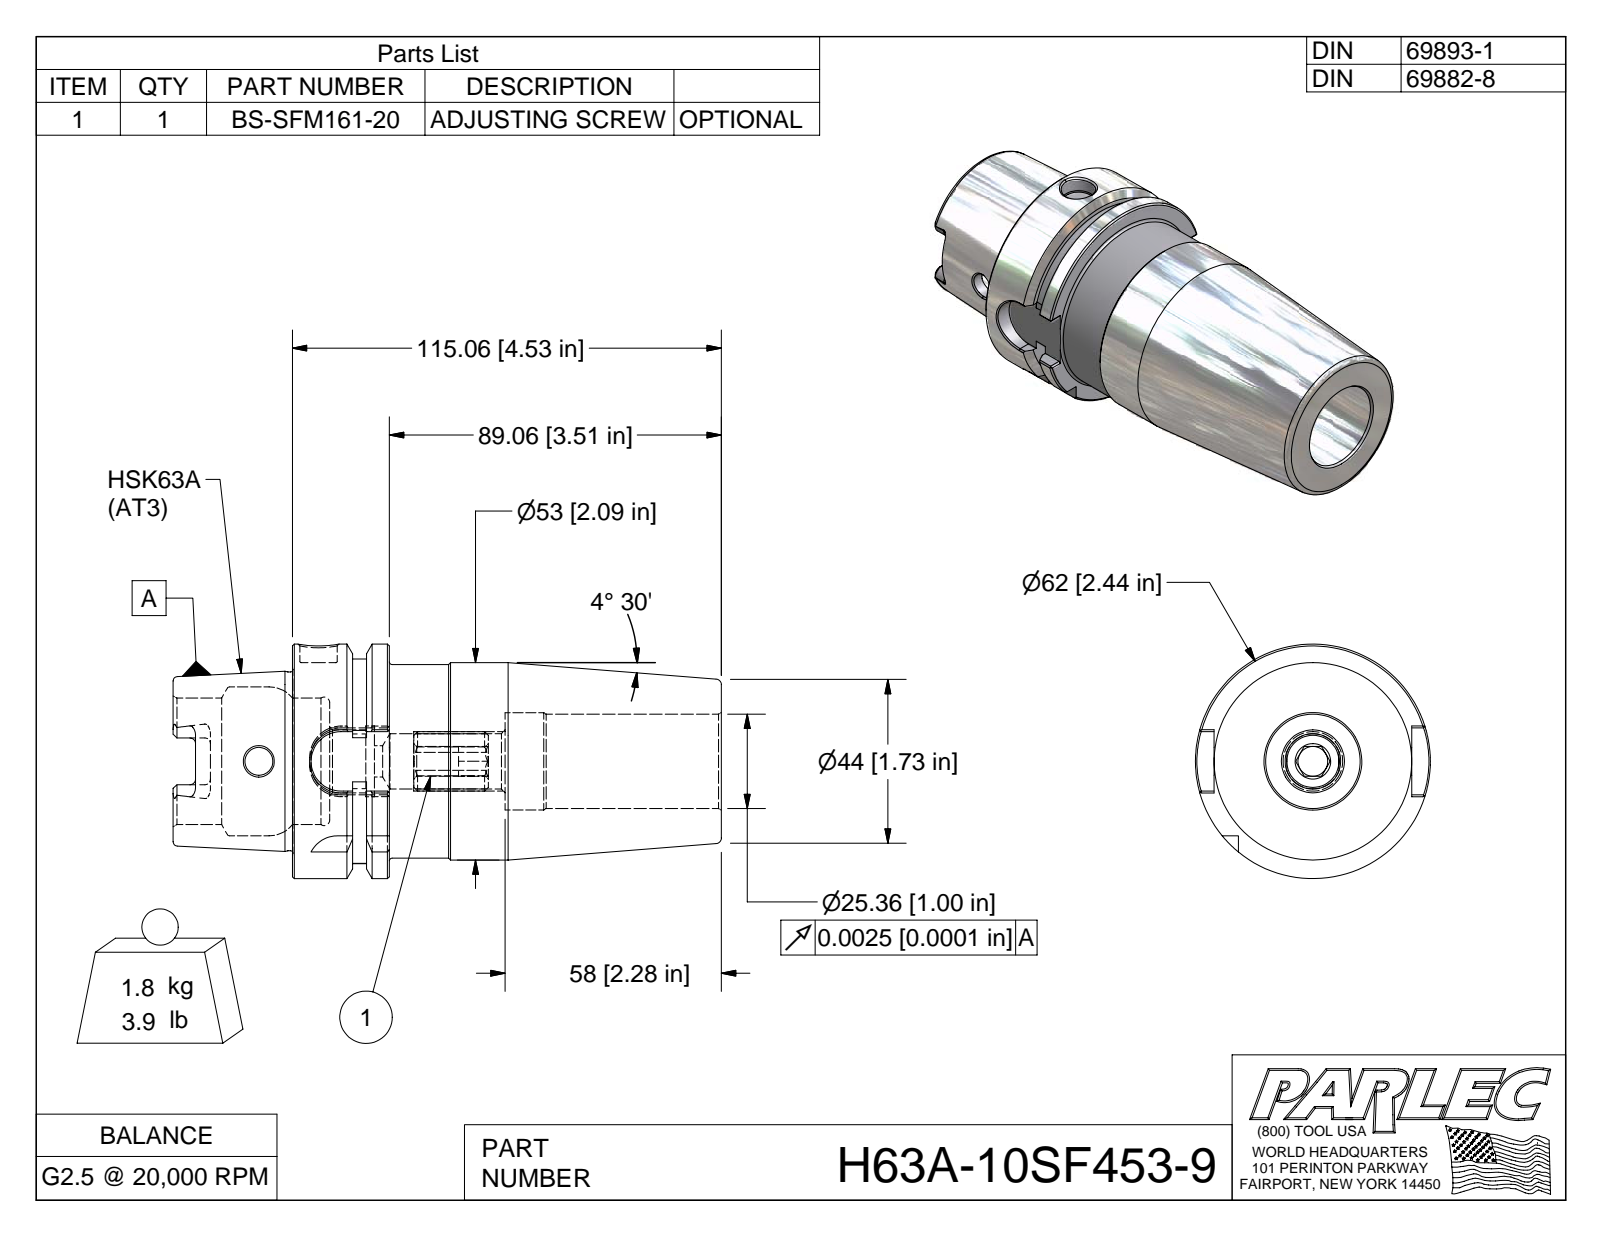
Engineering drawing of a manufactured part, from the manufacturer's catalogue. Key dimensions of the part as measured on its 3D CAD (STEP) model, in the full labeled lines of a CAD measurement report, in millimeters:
Part name (STEP PRODUCT): H63A-10SF453-9; H63A-10SF453-9-1; BS-SFM161-20
STEP written by: Autodesk Inventor 2009 (AUTOMOTIVE_DESIGN)
Units: millimetres
Bodies: 2 solids, 168 faces (66 planar, 37 cylindrical, 65 other)
Overall size (bounding box): 147.1 × 63 × 63
Volume: 223 500 mm³ · Surface area: 43 590 mm²
Round holes (diameter × count): ⌀7.5 ×1, ⌀10 ×1, ⌀16.9 ×1, ⌀19 ×1, ⌀25.4 ×1, ⌀26.1 ×1, ⌀34 ×1, ⌀40 ×1
Round bosses / shafts (diameter × count): ⌀63 ×1, ⌀53 ×1, ⌀52 ×1, ⌀48 ×1
Partial cylindrical surfaces — rounded edges, fillets, slot ends (radius × count): R1.5 ×6, R8 ×5, R2.9 ×4, R27.5 ×1
Main face-to-face distances: 89.1, 115.1, 26, 58, 6.1, 9.9, 10, 16, 105.1, 32
